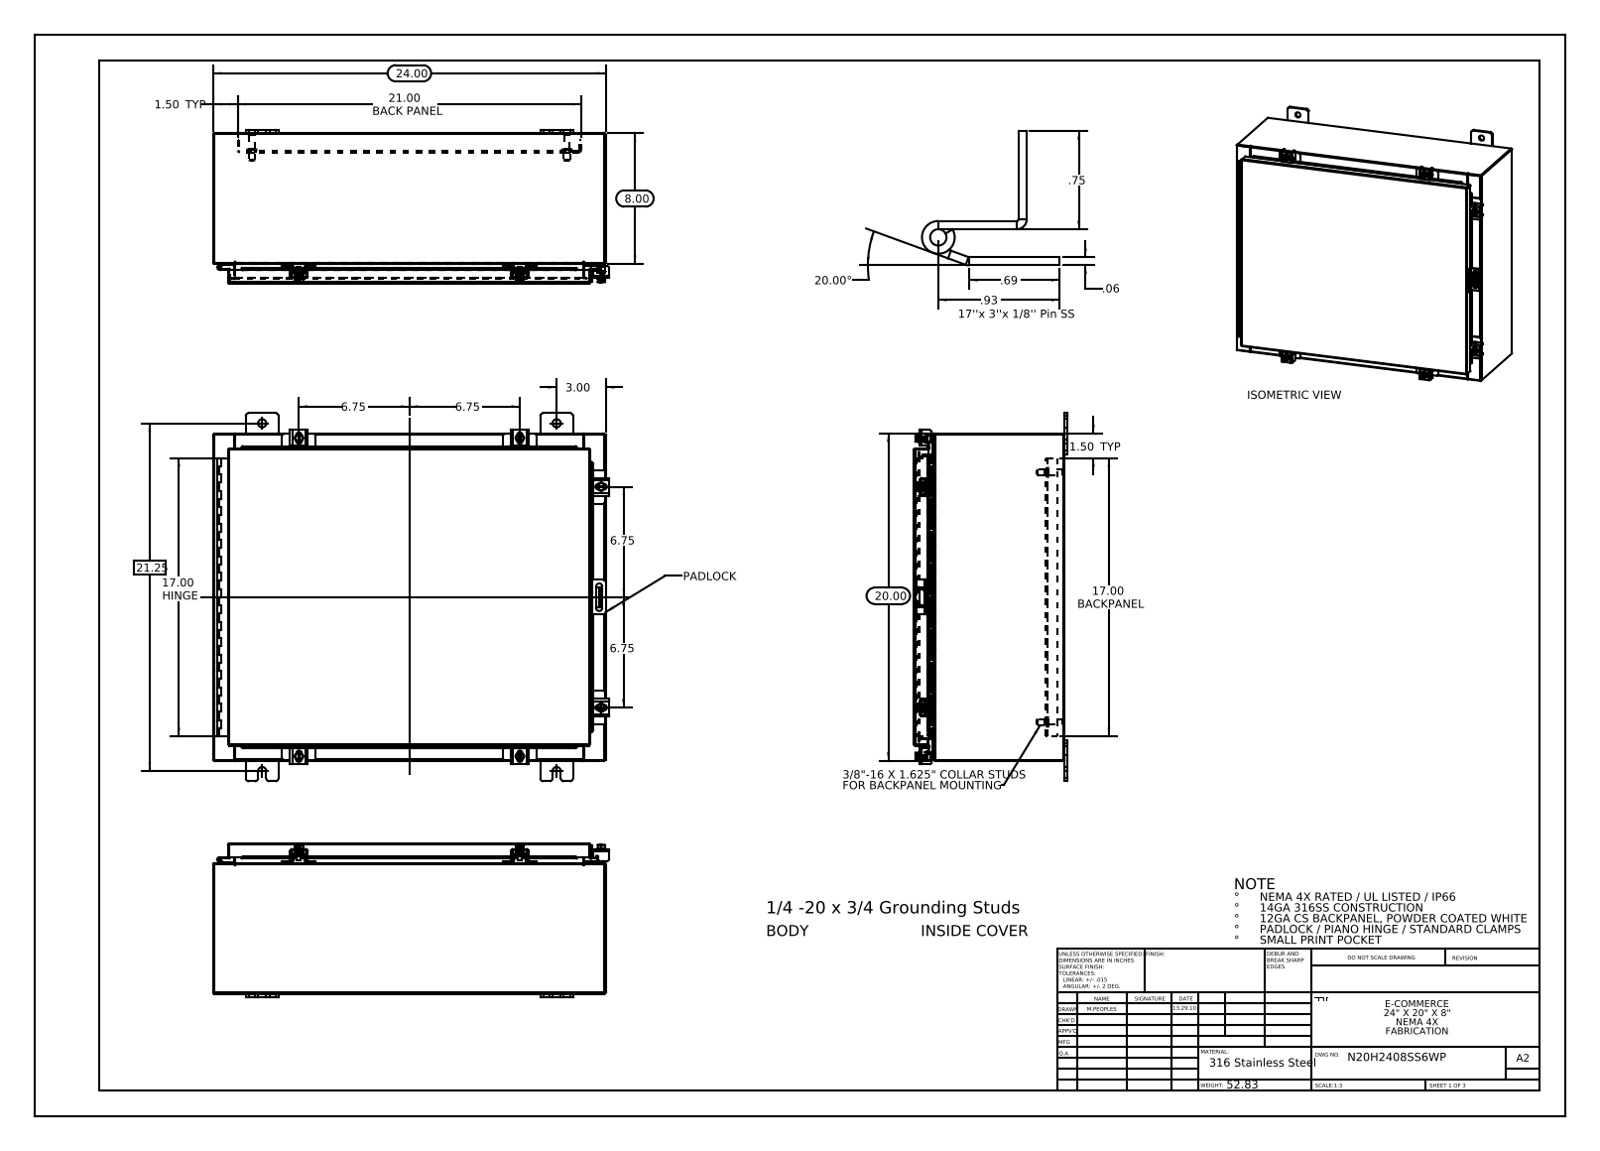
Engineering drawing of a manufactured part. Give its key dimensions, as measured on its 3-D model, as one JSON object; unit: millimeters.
{"part_name": "N20H2408SS6WP Mounting Studs; N20H2408SS6WP Clamp Assembly; N20H2408SS6WP Hinge Enclosure Side2; N20H2408SS6WP Standard Clamps (+8 more)", "step_written_by": "SolidWorks 2013 (CONFIG_CONTROL_DESIGN)", "units": "millimeters", "bodies": {"solids": 47, "faces": 1613, "planar": 860, "cylindrical": 657, "other": 96}, "overall_size": [615, 571.5, 238.5], "volume_mm3": 3046000, "surface_area_mm2": 3020000, "round_holes": [[12.7, 8], [5.4, 6], [6.6, 6], [3.2, 2], [3.2, 1]], "round_bosses_or_shafts": [[6.4, 7], [12.7, 6], [10.1, 6], [15.9, 4], [9.5, 4], [8.4, 4]], "partial_cylinders_radius": [[1.5, 30], [0.3, 25], [4.8, 24], [2.2, 21], [3, 12], [3.6, 12], [3.2, 10], [1.3, 9]], "face_to_face_distances": [1.9, 231.8, 233.7, 229.9, 506.1, 2.6, 25.4, 27.3, 204.5, 206.4], "hole_center_spacings": [446.7, 606, 342.9, 47.2, 57.8, 57.8, 61.5, 90.4]}
